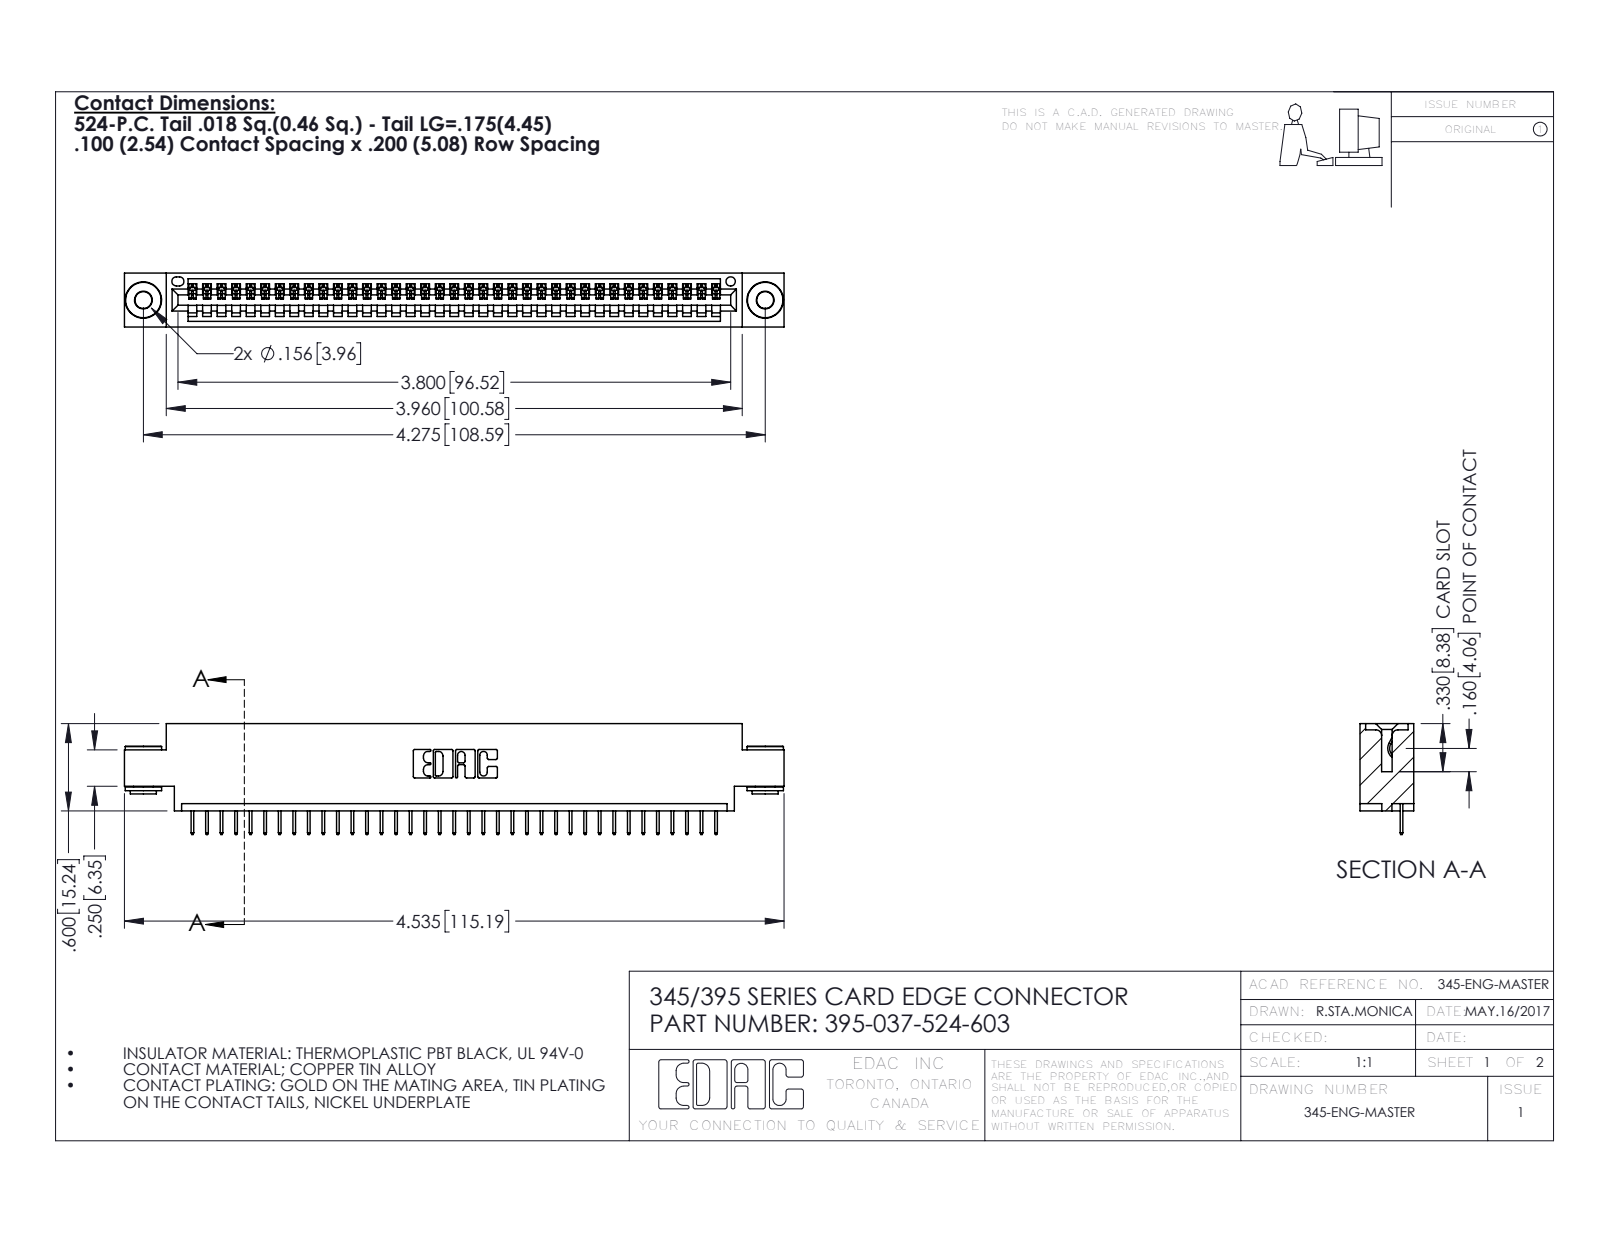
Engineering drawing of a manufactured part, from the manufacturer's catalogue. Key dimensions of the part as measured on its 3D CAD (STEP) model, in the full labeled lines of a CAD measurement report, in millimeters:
Part name (STEP PRODUCT): 345 Part_0.170 Offset - 0.156 Dia-TH; 345-250-002_345-250-002-102; 345-292-001_345-293-124; 395-037-524-603
STEP written by: SolidWorks 2016 (CONFIG_CONTROL_DESIGN)
Units: millimetres
Bodies: 40 solids, 2462 faces (1796 planar, 658 cylindrical, 8 other)
Overall size (bounding box): 115.2 × 19.4 × 9.4
Volume: 10 700 mm³ · Surface area: 13 970 mm²
Round holes (diameter × count): ⌀2.9 ×2, ⌀4 ×2, ⌀1.6 ×1
Round bosses / shafts (diameter × count): ⌀6.4 ×2, ⌀4.6 ×2, ⌀3.5 ×2
Partial cylindrical surfaces — rounded edges, fillets, slot ends (radius × count): R0.2 ×74, R0.3 ×22, R0.2 ×6, R0.8 ×6, R0.7 ×3, R0.8 ×2, R1 ×2, R0.4 ×1
Main face-to-face distances: 1.8, 7.6, 9.4, 5.1, 2.5, 6.9, 0.6, 5.7, 4.4, 1.8
Hole centre spacings: 6.9, 102.6, 108.6
